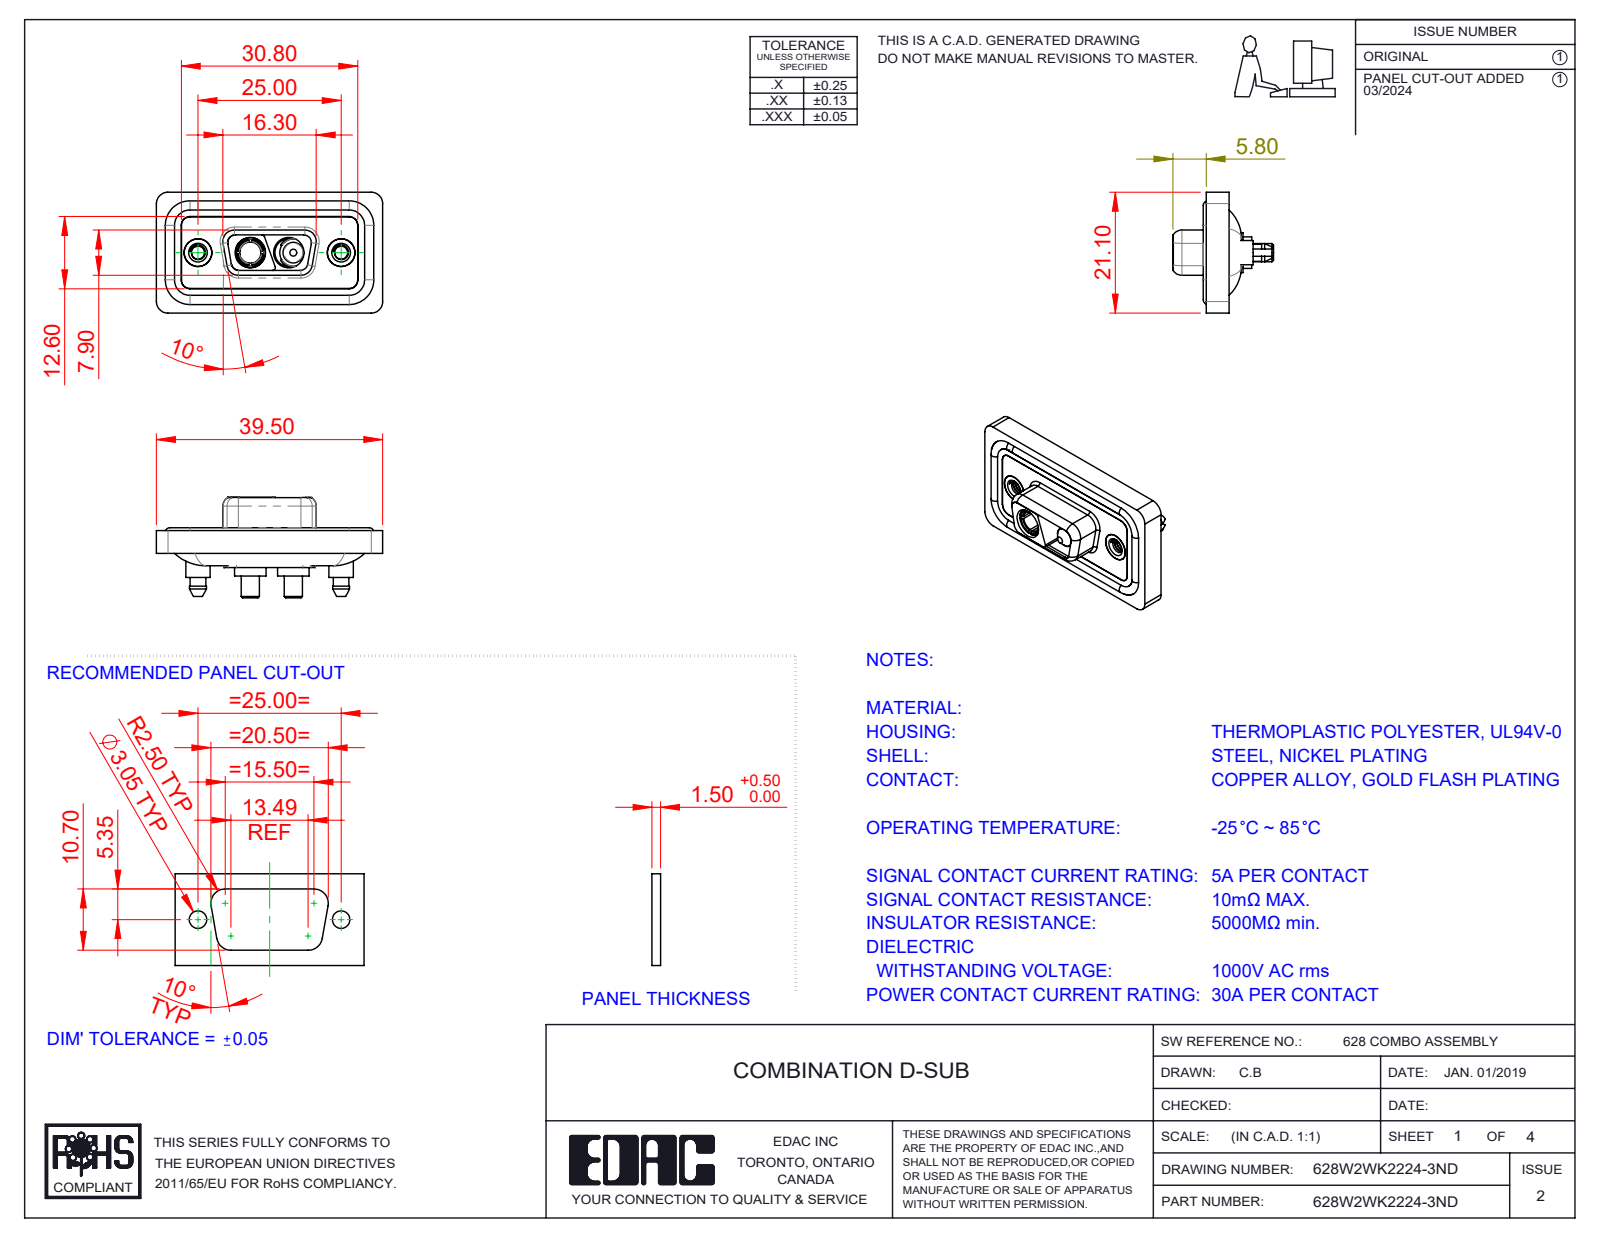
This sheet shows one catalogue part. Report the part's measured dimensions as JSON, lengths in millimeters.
{"part_name": "628Combo Housing_2WK2; Power Pin_30A S; 628Combo Shell Front_09 Contacts; 628Combo Waterproof Housing_09 Contacts (+4 more)", "step_written_by": "SolidWorks 2023 (CONFIG_CONTROL_DESIGN)", "units": "millimeters", "bodies": {"solids": 11, "faces": 566, "planar": 160, "cylindrical": 279, "other": 127}, "overall_size": [39.5, 21.1, 17.55], "volume_mm3": 4753, "surface_area_mm2": 7692, "round_holes": [[4.85, 4], [2.26, 2], [4, 2], [4.05, 2], [5, 2], [5.3, 2], [3.7, 1]], "round_bosses_or_shafts": [[1.6, 4], [5.5, 2], [5.4, 2], [5.2, 2], [4.95, 2], [4.8, 2], [4.75, 2], [4.25, 2]], "partial_cylinders_radius": [[1.5, 24], [2, 18], [1.6, 10], [1.35, 8], [0.5, 6], [0.25, 4], [0.6, 4], [0.65, 4]], "face_to_face_distances": [0.4, 1.1, 2.9, 1.6, 0.5, 1.8, 5.65, 1.5, 4, 5.35], "hole_center_spacings": [9.14, 15.86, 6.72, 25]}
